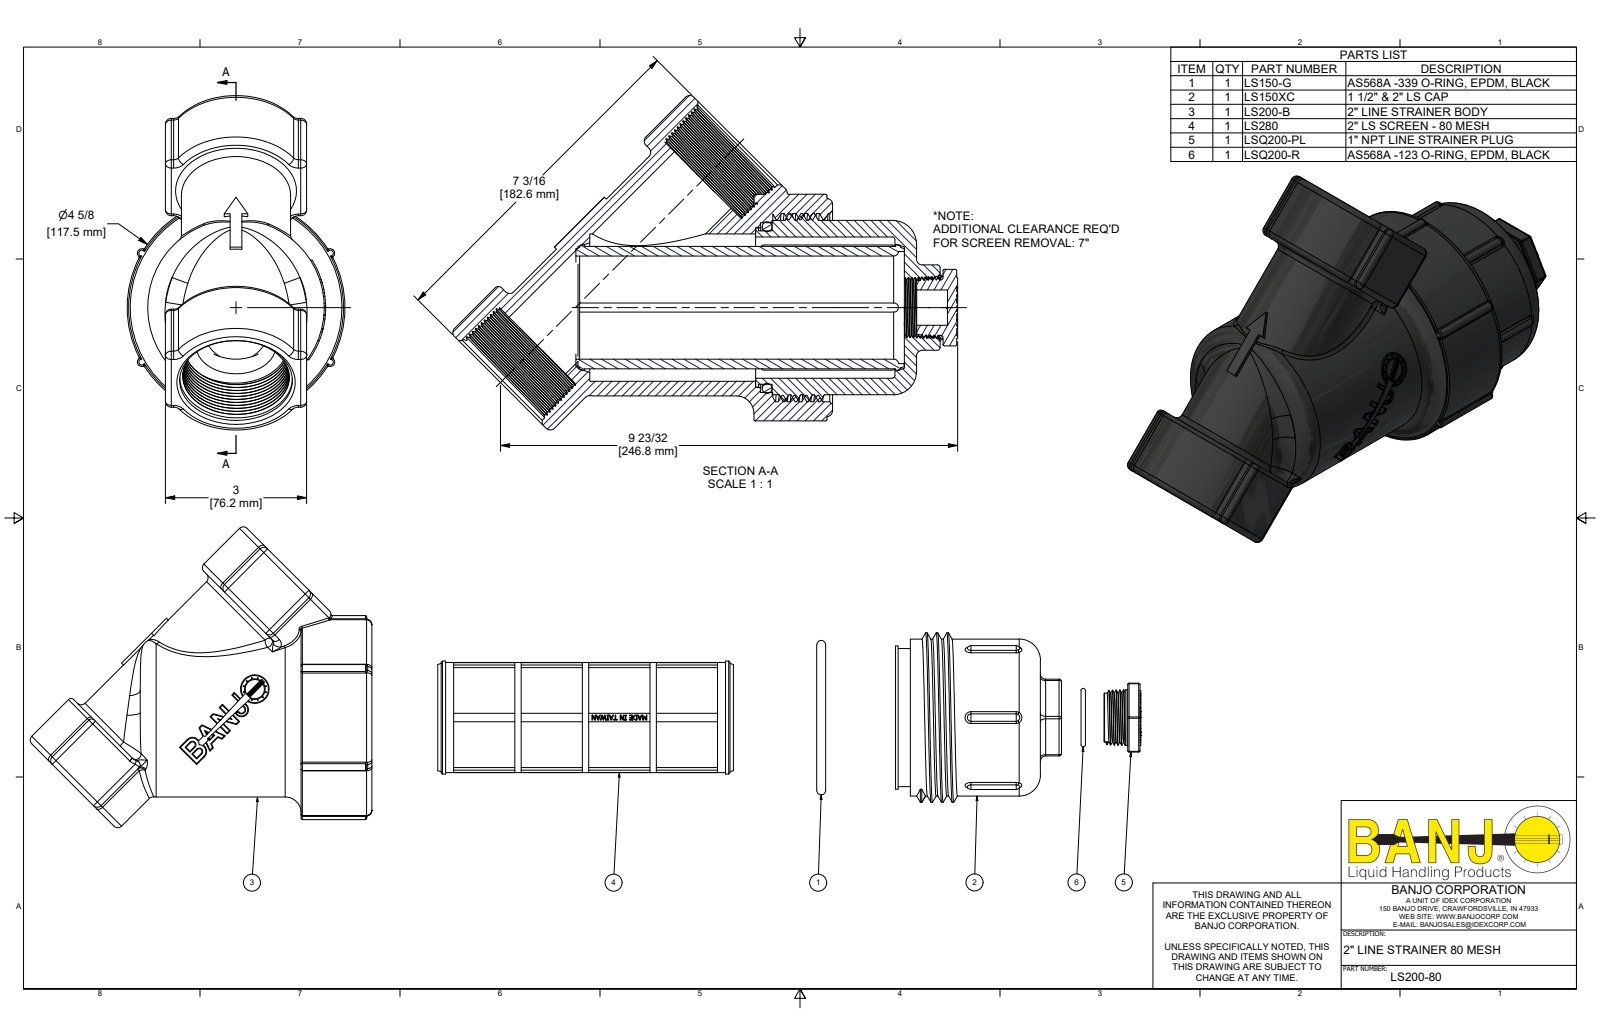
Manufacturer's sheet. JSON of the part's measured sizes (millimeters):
{"part_name": "LS200-80; LS200-B; LS150-C; LS150XC (+4 more)", "step_written_by": "Autodesk Inventor 2022 (AUTOMOTIVE_DESIGN)", "units": "millimeters", "bodies": {"solids": 6, "faces": 1754, "planar": 841, "cylindrical": 277, "other": 636}, "overall_size": [272.4, 180.4, 117.5], "volume_mm3": 886900, "surface_area_mm2": 311300, "round_holes": [[43.2, 2], [11.5, 1], [16.3, 1], [19.1, 1], [55.6, 1], [59.7, 1], [76.2, 1], [79.5, 1], [86.2, 1], [91.6, 1], [94.7, 1], [101.6, 1]], "round_bosses_or_shafts": [[117.5, 1], [95.3, 1], [94, 1], [85.9, 1], [82.7, 1], [67.7, 1], [66, 1], [60.5, 1]], "partial_cylinders_radius": [[1.5, 46], [3.2, 34], [0.8, 30], [2.4, 11], [2.5, 4], [2.3, 3], [1.7, 2], [2.1, 2]], "face_to_face_distances": [34, 6.6, 76.2, 80.3, 70.7, 6.4, 36.7, 98.4, 5.1, 8.9]}
